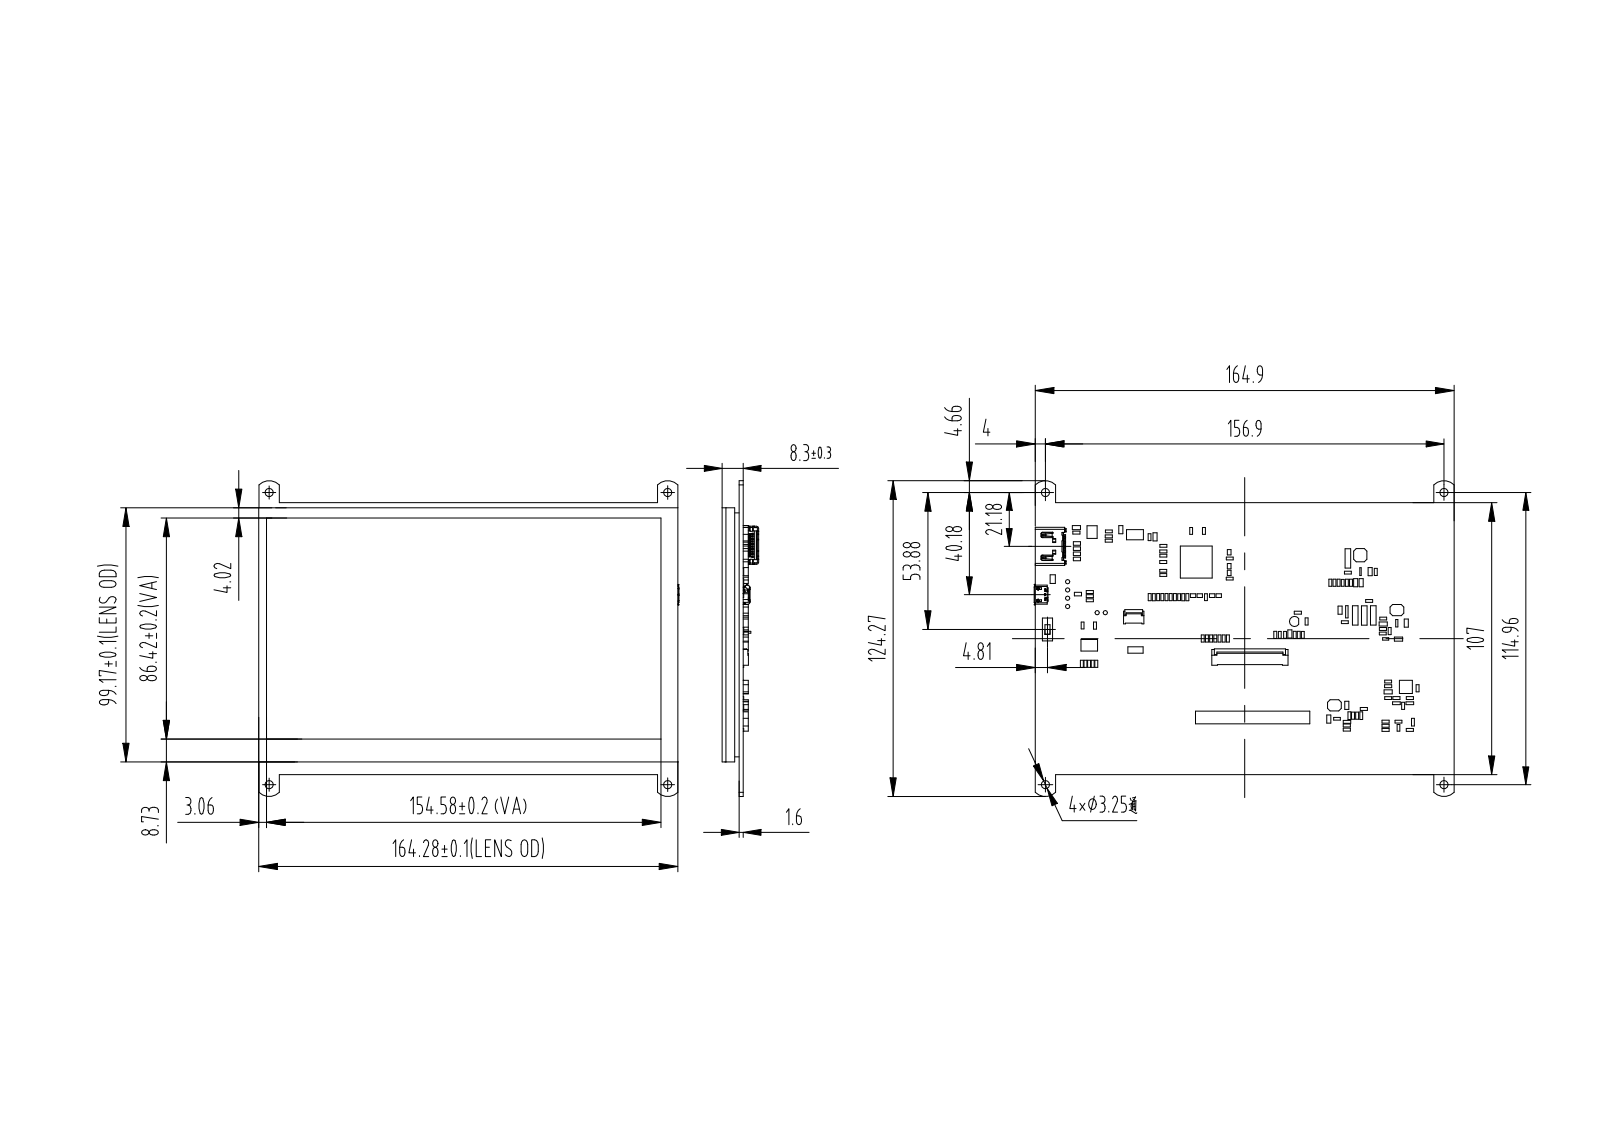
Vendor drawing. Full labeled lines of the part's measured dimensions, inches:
Part name (STEP PRODUCT): 7inch HDMI LCD (B); 000; 000_1; USB_J17INCH_HDMI_L0001 (+1 more)
STEP written by: ZW3D to STEP translator (AUTOMOTIVE_DESIGN)
Units: inches
Bodies: 149 solids, 2567 faces (2175 planar, 384 cylindrical, 8 other)
Overall size (bounding box): 6.513 × 4.893 × 0.566
Volume: 7.52 in³ · Surface area: 173.7 in²
Round holes (diameter × count): ⌀0.128 ×4
Round bosses / shafts (diameter × count): ⌀0.067 ×6, ⌀0.157 ×1
Partial cylindrical surfaces — rounded edges, fillets, slot ends (radius × count): R0.008 ×32, R0.01 ×23, R0.006 ×20, R0.02 ×18, R0.012 ×13, R0.004 ×10, R0.016 ×10, R0.022 ×8
Main face-to-face distances: 0.205, 0.063, 0.268, 0.053, 0.321, 0.258, 0.069, 0.189, 0.136, 0.132
Hole centre spacings: 4.526, 6.177, 7.658
